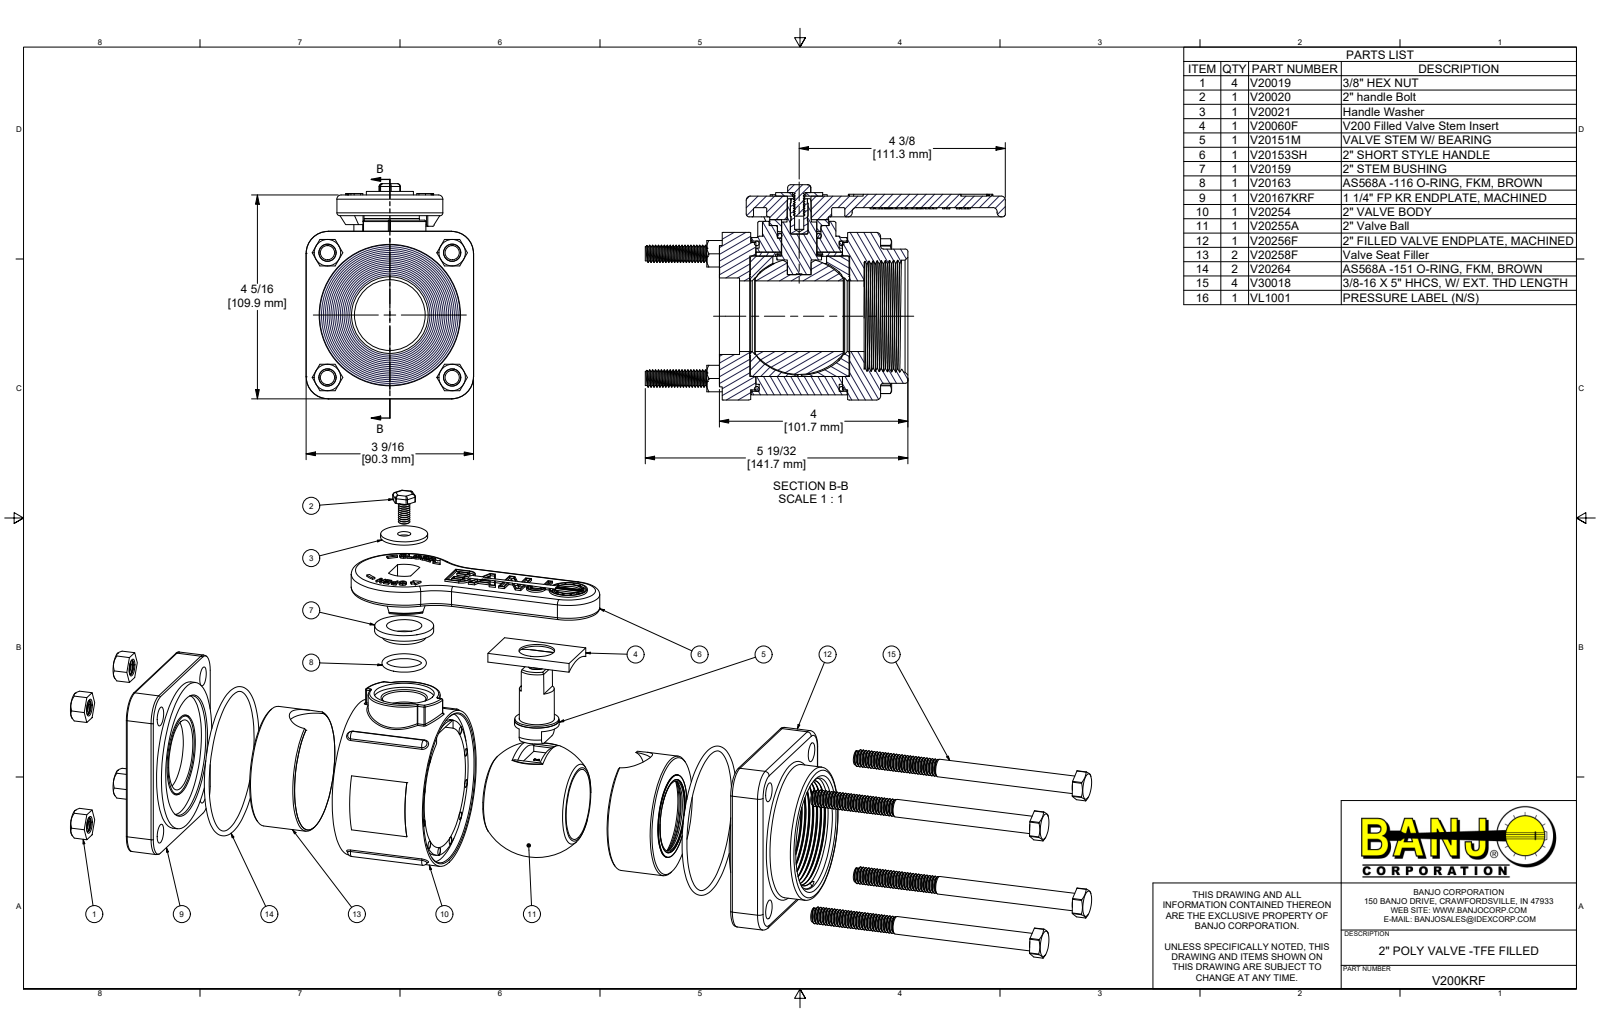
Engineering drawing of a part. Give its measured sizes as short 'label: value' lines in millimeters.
name: V20019; V20020; V20021; V20060F (+8 more)
written by: Autodesk Inventor 2015 (AUTOMOTIVE_DESIGN)
unit: mm
bodies: 26 solids, 1557 faces (615 planar, 467 cylindrical, 475 other)
size: 194.31 × 116.1 × 90.42
volume: 552 696 mm³; area: 191 611 mm²
holes: 10× ⌀4.19, 5× ⌀9.52, 4× ⌀7.81, 4× ⌀10.31, 1× ⌀4.98, 1× ⌀7.14, 1× ⌀8.92, 1× ⌀13.83, 1× ⌀19.05, 1× ⌀19.08, 1× ⌀19.3, 1× ⌀19.55
bosses: 4× ⌀9.22, 4× ⌀7.63, 1× ⌀79.5, 1× ⌀76.2, 1× ⌀73.41, 1× ⌀67.31, 1× ⌀57.15, 1× ⌀44.86
rounds: 30× R0.76, 22× R2.29, 10× R1.52, 9× R3.17, 4× R0.38, 4× R2.38, 4× R8.12, 4× R11.91
face distances: 2.79, 49.53, 90.42, 85.47, 17.78, 15.37, 8.89, 67.69, 52.32, 70.1
hole spacings: 34.61, 58.82, 66.86, 17.91, 24.67, 42.59, 59.94, 71.45
